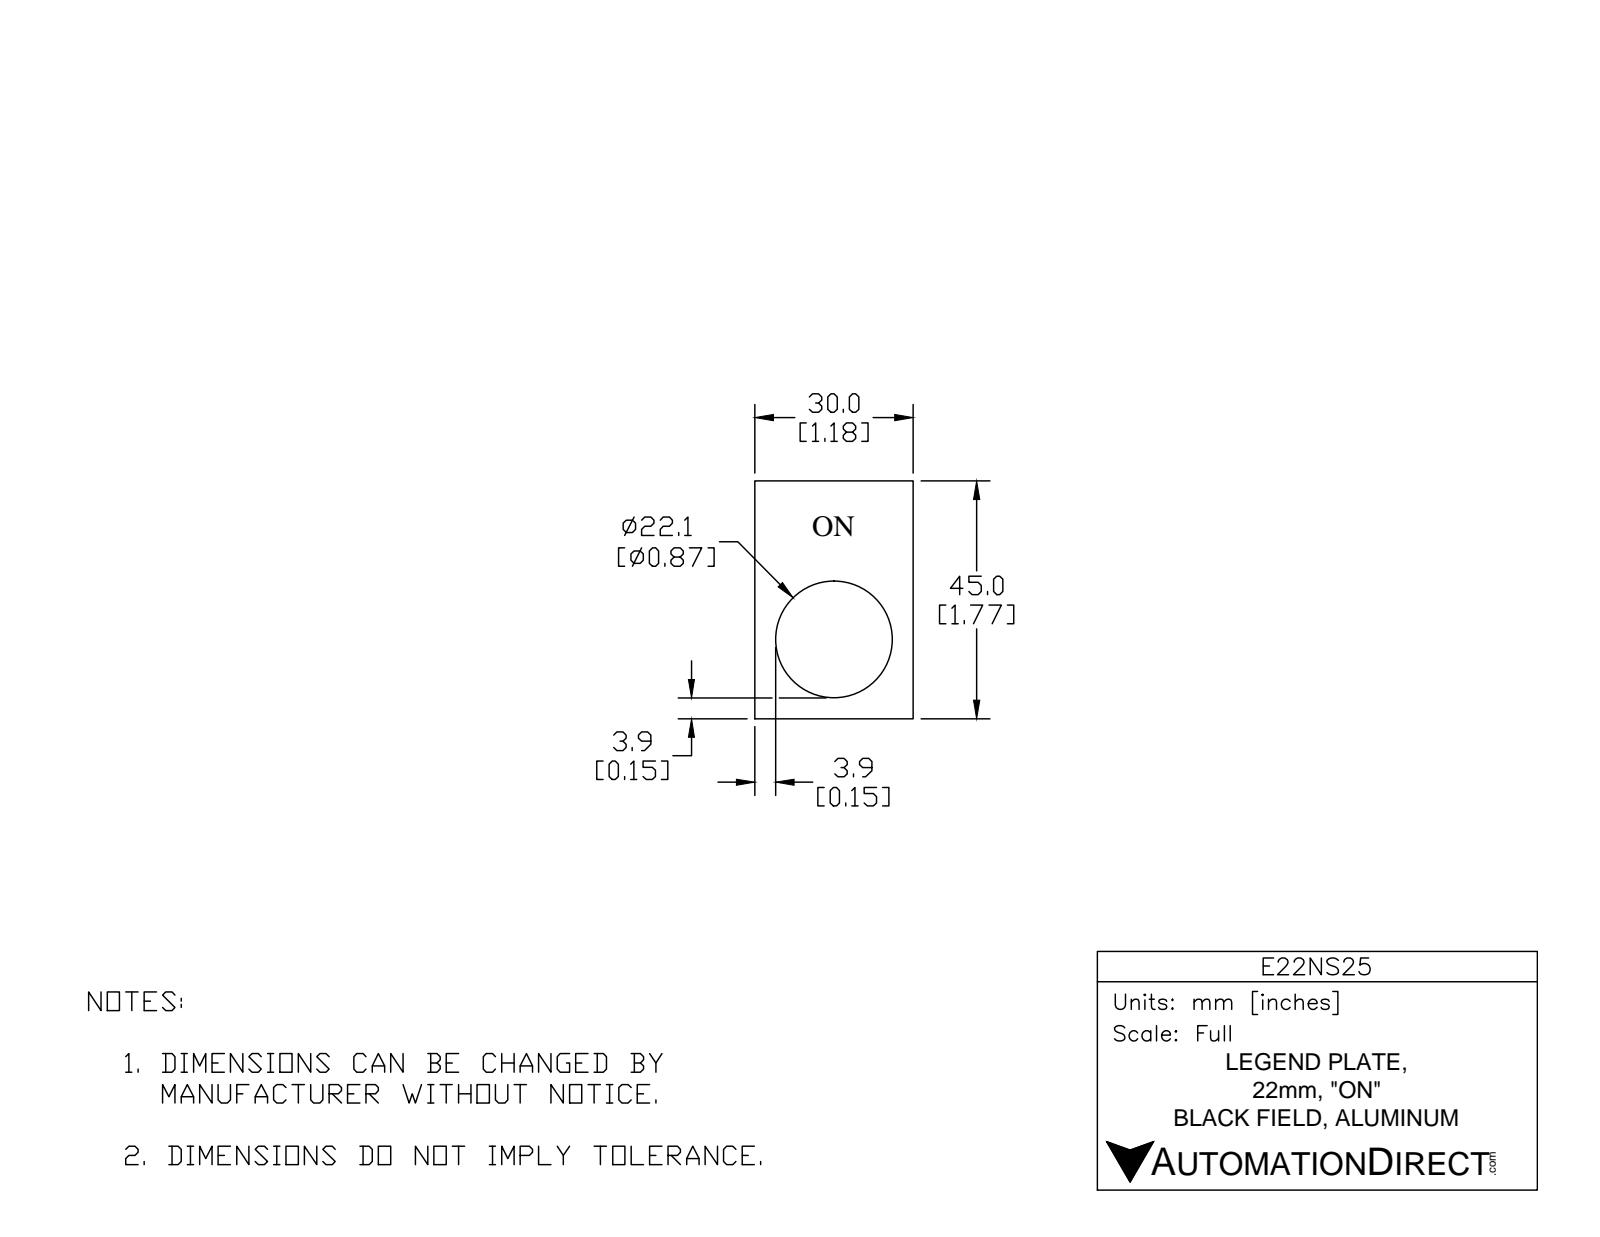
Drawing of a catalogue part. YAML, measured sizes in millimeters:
part_name: "E22NS25"
step_written_by: "SolidWorks 2017 (AUTOMOTIVE_DESIGN)"
units: millimeters
bodies: {solids: 1, faces: 33, planar: 22, cylindrical: 3, other: 8}
overall_size: [45, 30, 1.3]
volume: 1253
surface_area: 2230
round_holes:
  - {diameter: 22.2, count: 1}
face_to_face_distances: [1.3, 30, 45, 1.05, 4.7, 40.3, 13.4, 16.6, 0.36, 2.72]
